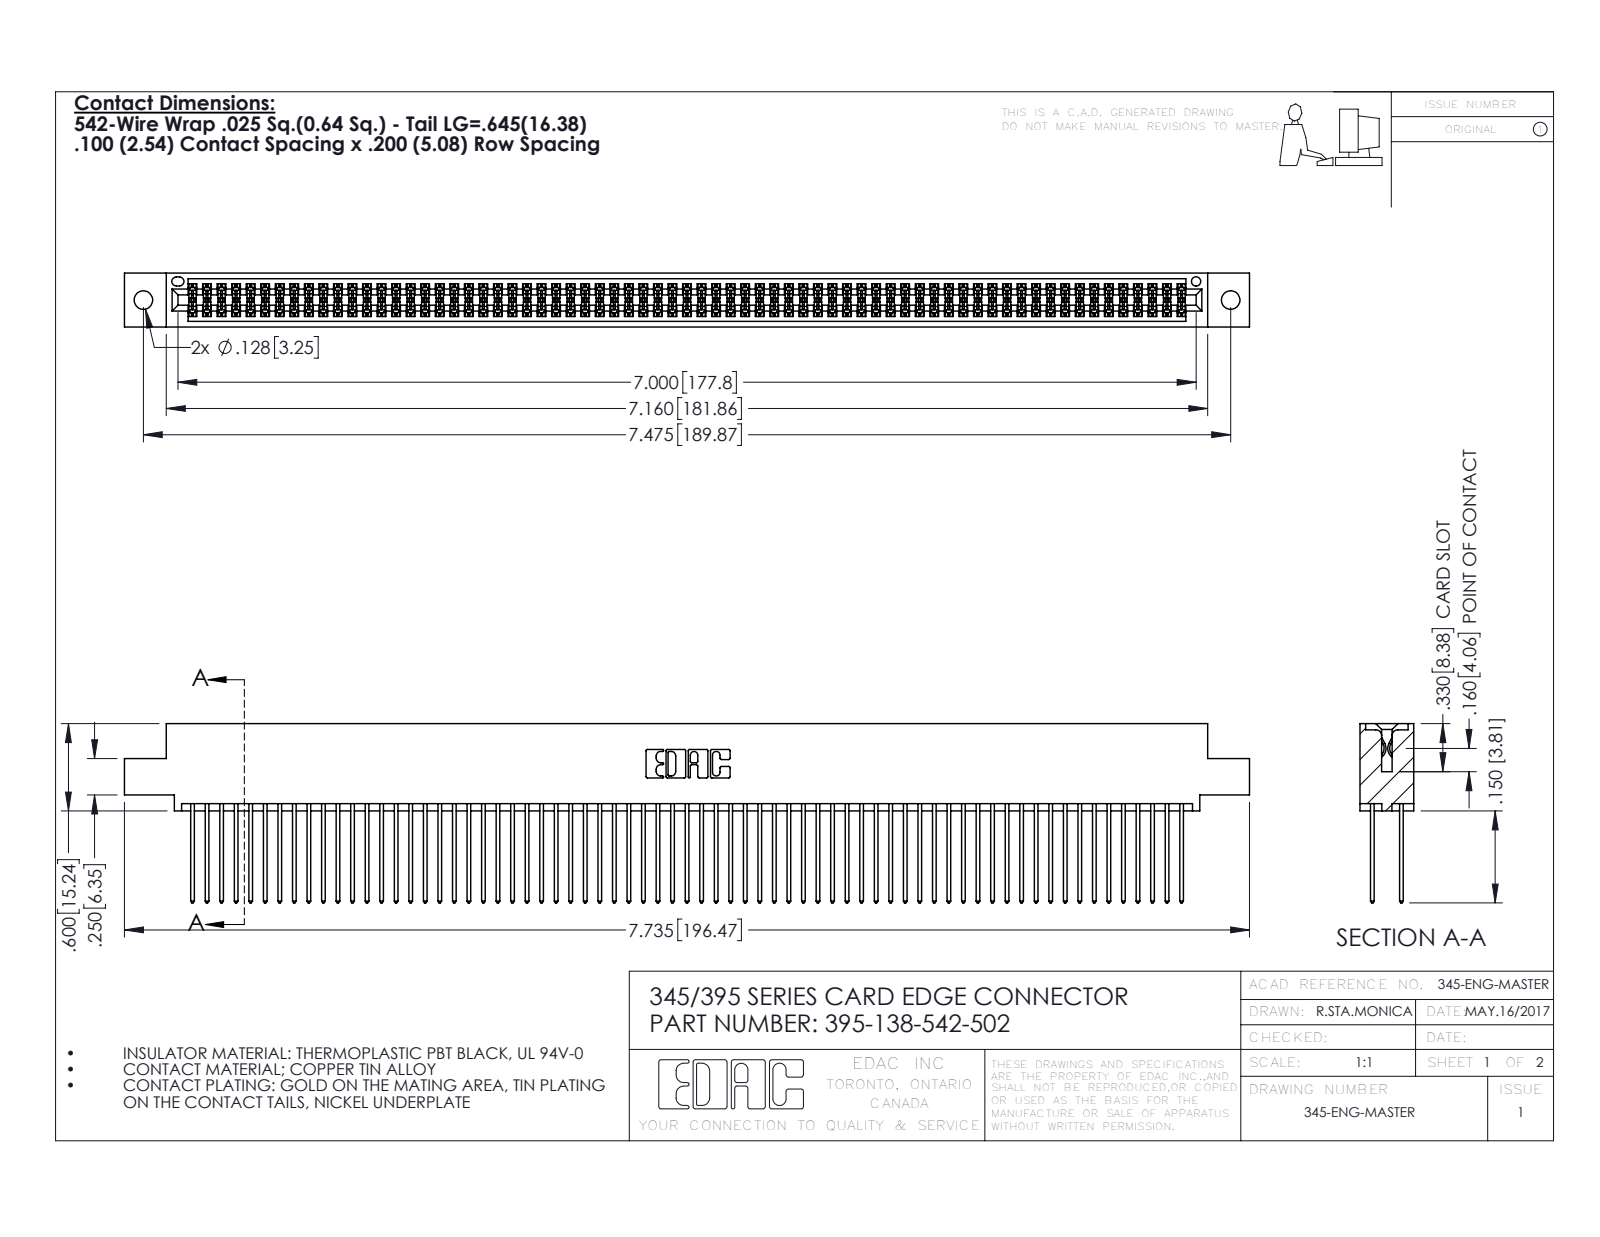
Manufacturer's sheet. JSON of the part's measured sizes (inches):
{"part_name": "395-138-542-502; 345 Part_0.110 Offset - 0.128 Dia; 345-292-001_345-293-142", "step_written_by": "SolidWorks 2016 (CONFIG_CONTROL_DESIGN)", "units": "inches", "bodies": {"solids": 139, "faces": 7030, "planar": 4638, "cylindrical": 2392, "other": 0}, "overall_size": [7.735, 1.232, 0.37], "volume_in3": 1.212, "surface_area_in2": 50.71, "round_holes": [[0.128, 2], [0.064, 1]], "partial_cylinders_radius": [[0.006, 207], [0.01, 138], [0.01, 22], [0.007, 6], [0.031, 6], [0.026, 3], [0.014, 2], [0.019, 2]], "face_to_face_distances": [0.072, 0.298, 0.2, 0.098, 0.272, 0.025, 0.225, 0.37, 0.175, 0.149], "hole_center_spacings": [0.27, 7.239, 7.475]}
